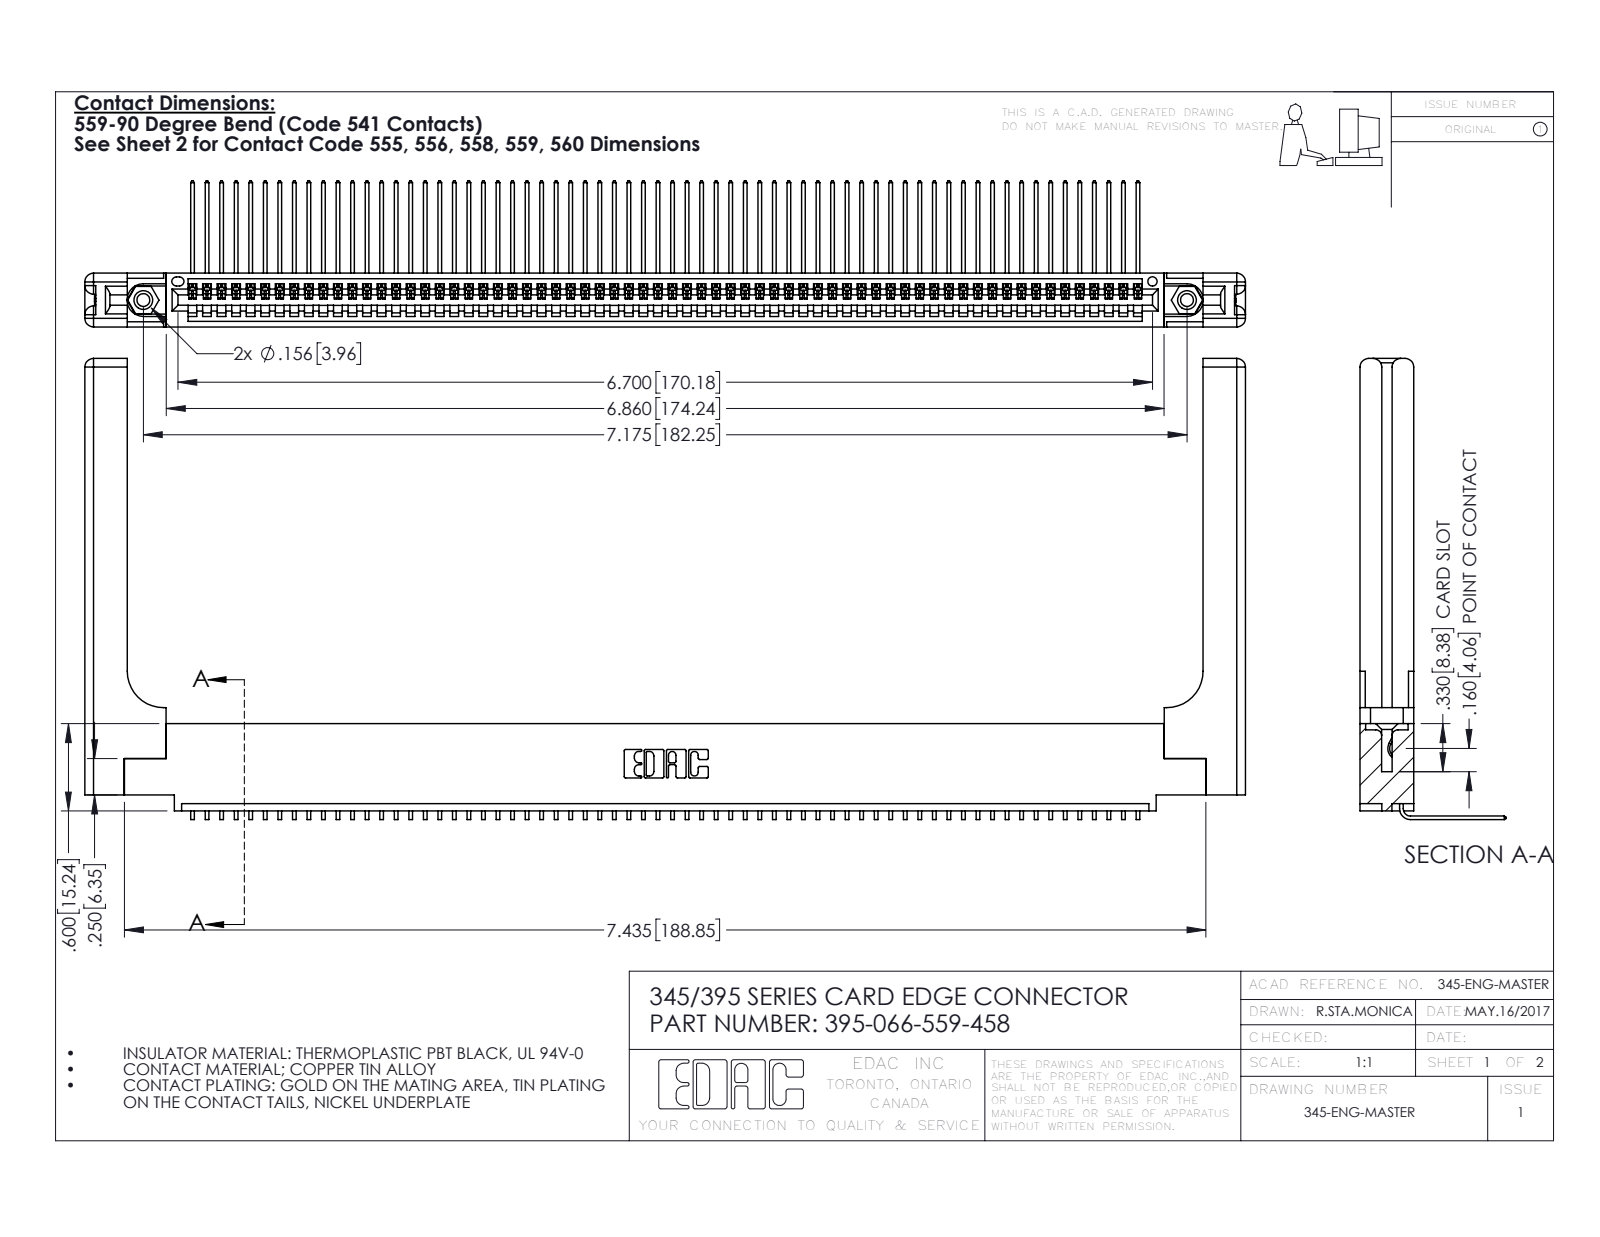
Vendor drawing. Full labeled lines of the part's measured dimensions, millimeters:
Part name (STEP PRODUCT): 345 Part_0.110 Offset - 0.156 Dia-TH; 345-292-001_558 559 Tail - 1; 345-250-001_345-250-001-102; 345-220-058_345-220-058 (+1 more)
STEP written by: SolidWorks 2016 (CONFIG_CONTROL_DESIGN)
Units: millimetres
Bodies: 71 solids, 4346 faces (3004 planar, 1282 cylindrical, 60 other)
Overall size (bounding box): 202.7 × 80.5 × 25.5
Volume: 28 100 mm³ · Surface area: 33 050 mm²
Round holes (diameter × count): ⌀2.3 ×2, ⌀3.2 ×2, ⌀4 ×2, ⌀1.6 ×1
Round bosses / shafts (diameter × count): ⌀3.9 ×2
Partial cylindrical surfaces — rounded edges, fillets, slot ends (radius × count): R0.2 ×132, R0.3 ×22, R1.5 ×16, R0.2 ×6, R0.8 ×6, R0.7 ×3, R0.8 ×2, R0.8 ×2
Main face-to-face distances: 1.8, 9.4, 7.6, 2.5, 6.9, 0.6, 5.1, 5.7, 3.8, 3.8
Hole centre spacings: 6.9, 176.3, 182.2
